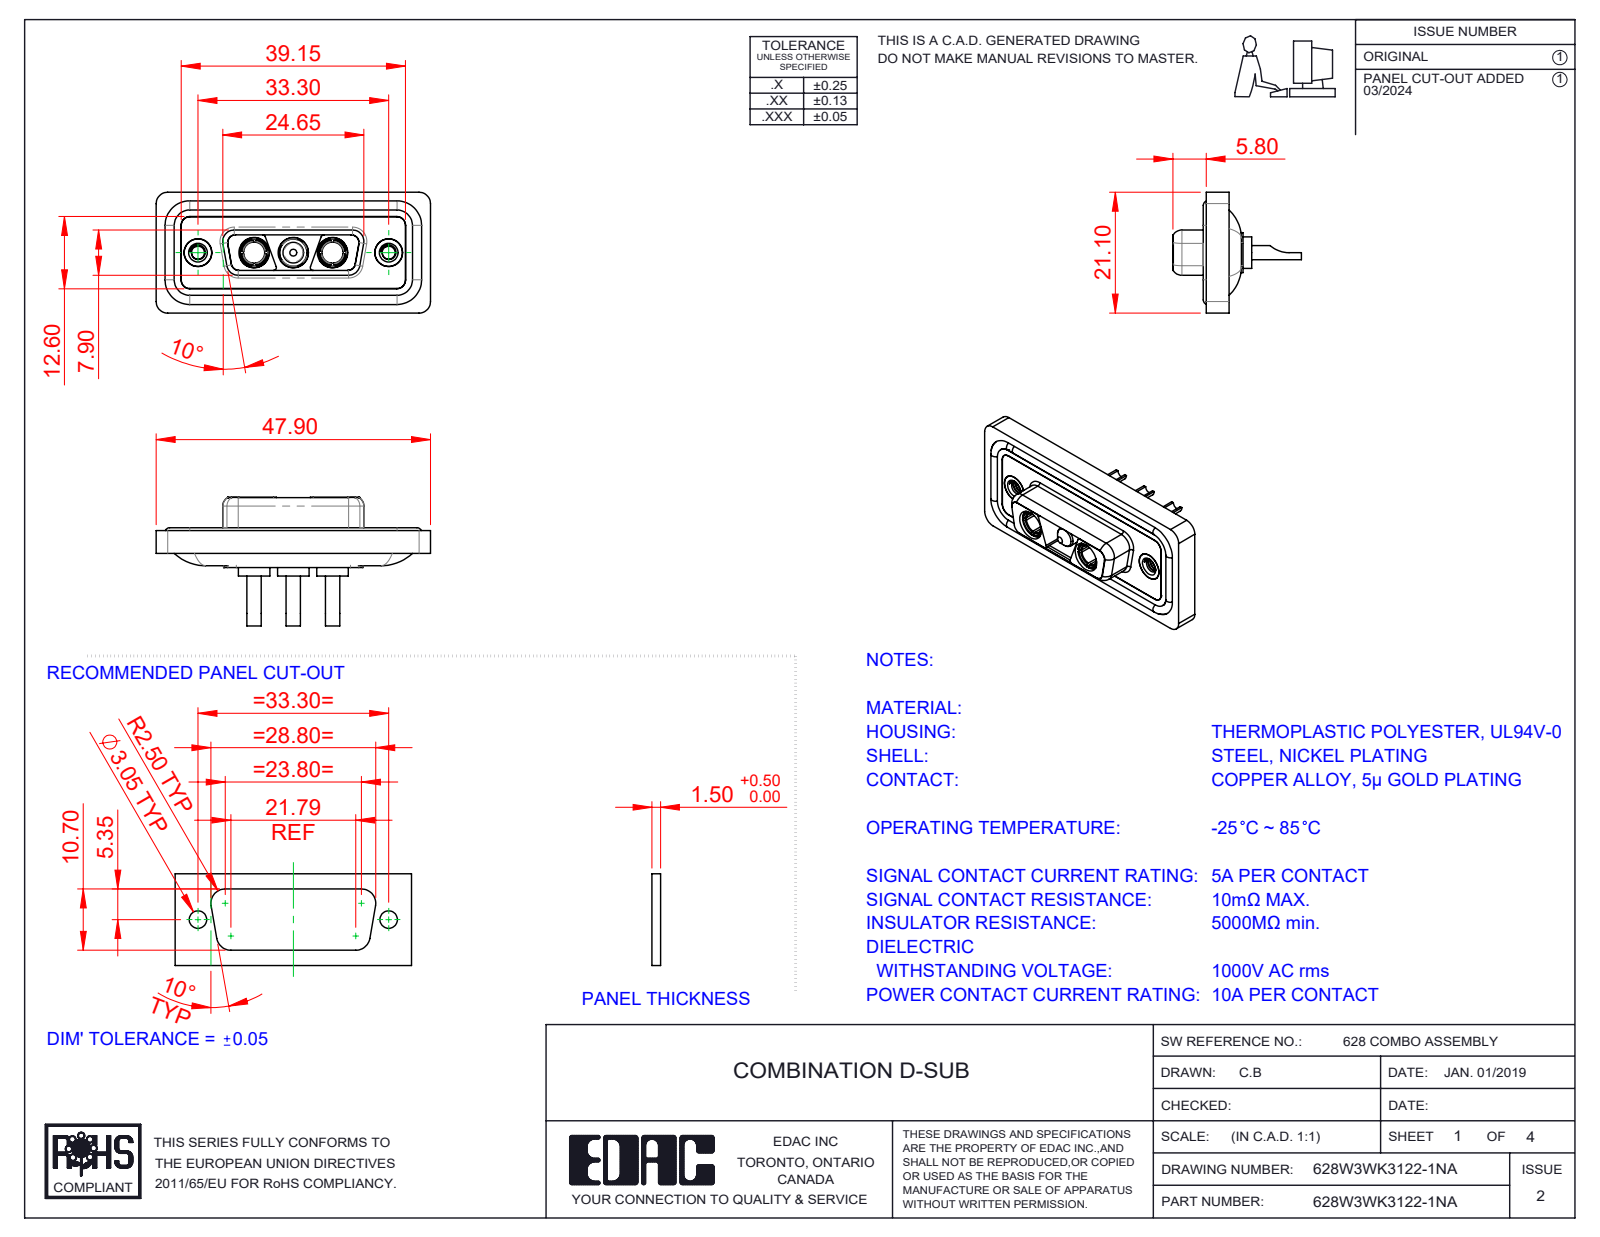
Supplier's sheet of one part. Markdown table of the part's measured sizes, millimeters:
| quantity | value |
| --- | --- |
| part name | 628Combo Shell Rear_15 Contacts; 628Combo Housing_3WK3; 628Combo Threaded Rivet_A; Power Pin_10A SC (+4 more) |
| STEP written by | SolidWorks 2023 (CONFIG_CONTROL_DESIGN) |
| units | millimeters |
| bodies | 13 solids, 597 faces (184 planar, 269 cylindrical, 144 other) |
| overall size | 47.9 × 22.45 × 21.1 |
| volume | 5 871 mm³ |
| surface area | 9 645 mm² |
| round holes (diameter × count) | 4.85 × 5, 1.7 × 3, 5.3 × 3, 2.26 × 2, 3.7 × 2, 4 × 2, 4.05 × 2, 5 × 2 |
| round bosses / shafts (diameter × count) | 1.6 × 4, 5.5 × 3, 5.2 × 3, 4.75 × 3, 3.75 × 3, 2.5 × 3, 4.96 × 2, 4.95 × 2 |
| partial cylindrical surfaces (radius × count) | 1.5 × 22, 2 × 20, 1.35 × 12, 0.5 × 8, 1.6 × 8, 0.25 × 4, 0.6 × 4, 0.65 × 4 |
| main face-to-face distances | 0.4, 1.6, 1.8, 0.5, 1.1, 2.9, 5.65, 7.05, 1.5, 5.35 |
| hole center spacings | 6.85, 9.8, 16.65, 23.5, 13.7, 33.3 |
